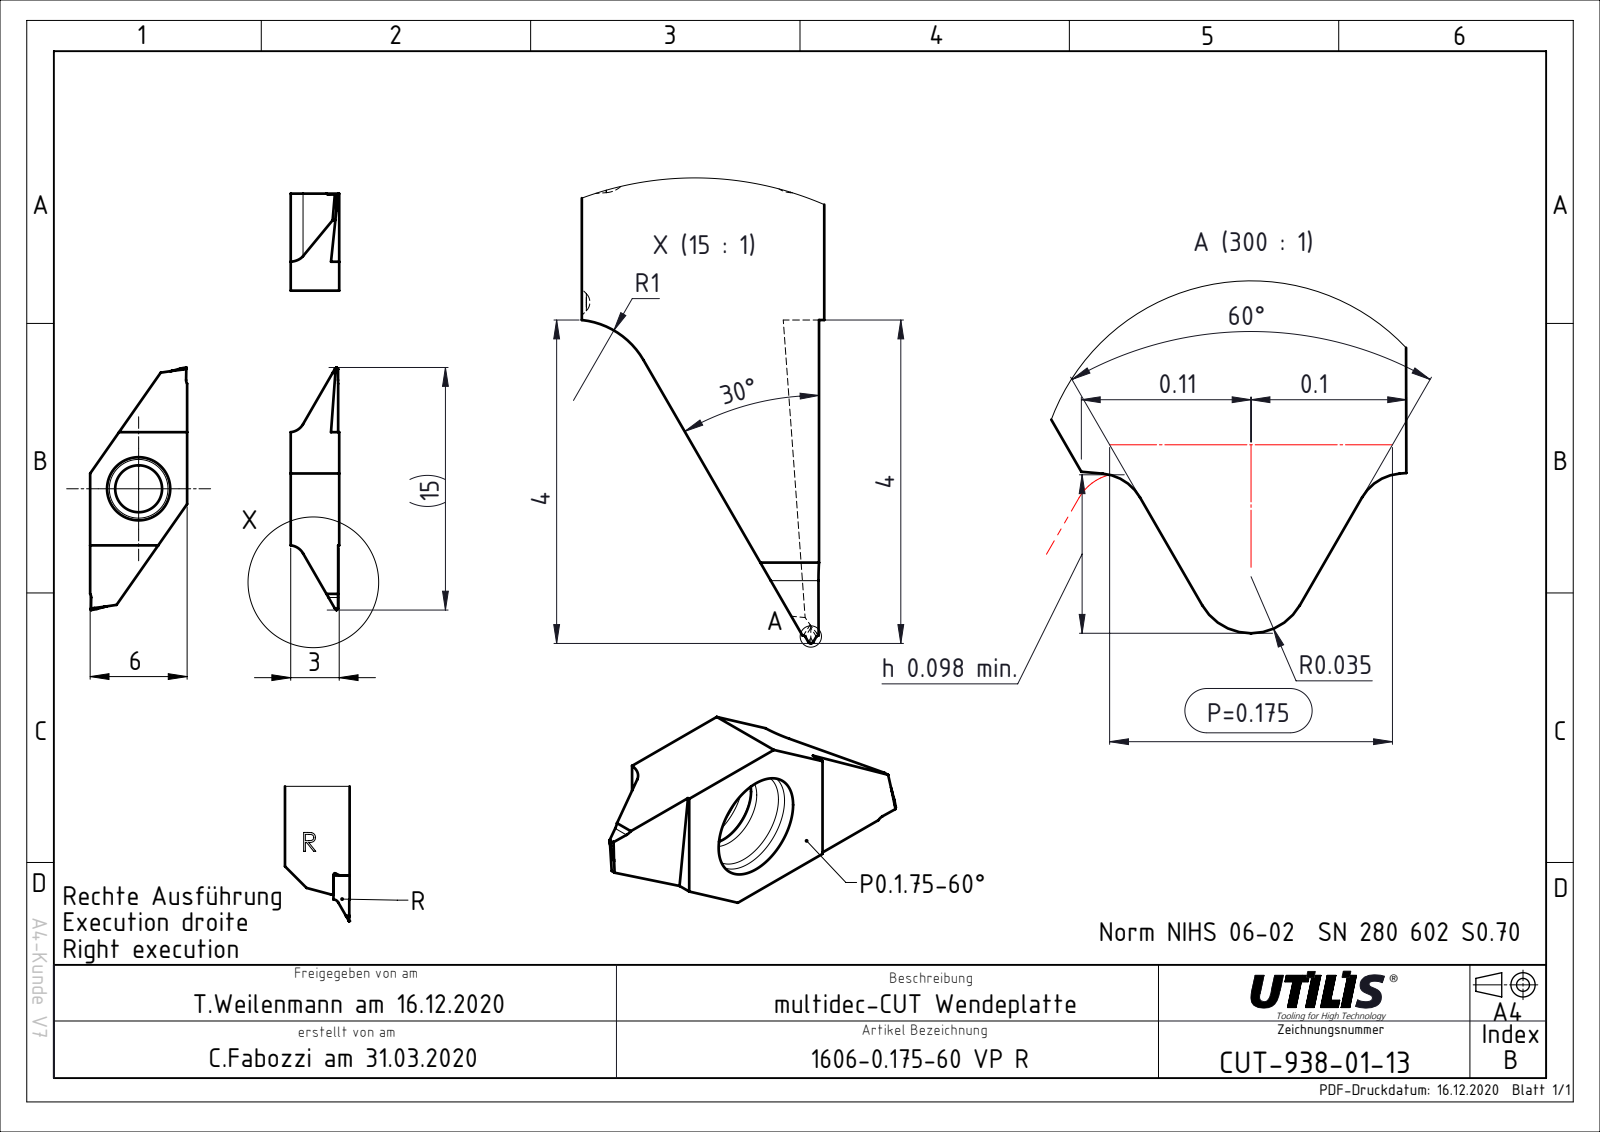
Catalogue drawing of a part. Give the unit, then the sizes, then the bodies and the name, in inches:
Units: inches
Overall size (bounding box): 0.591 × 0.236 × 0.118
Round holes (diameter × count): ⌀0.114 ×1
Partial cylindrical surfaces — rounded edges, fillets, slot ends (radius × count): R0.039 ×2
Main face-to-face distances: 0.236, 0.118, 0.354, 0.276, 0.472, 0.284, 0.568, 0.569
Volume: 0.008 in³ · Surface area: 0.324 in²
Bodies: 1 solid, 36 faces (22 planar, 14 cylindrical, 0 other)
Part name (STEP PRODUCT): CUT-938-01; ASME Y14.5
STEP written by: FormatWorks Professional (AP242_MANAGED_MODEL_BASED_3D_ENGINEERING_MIM_LF)
